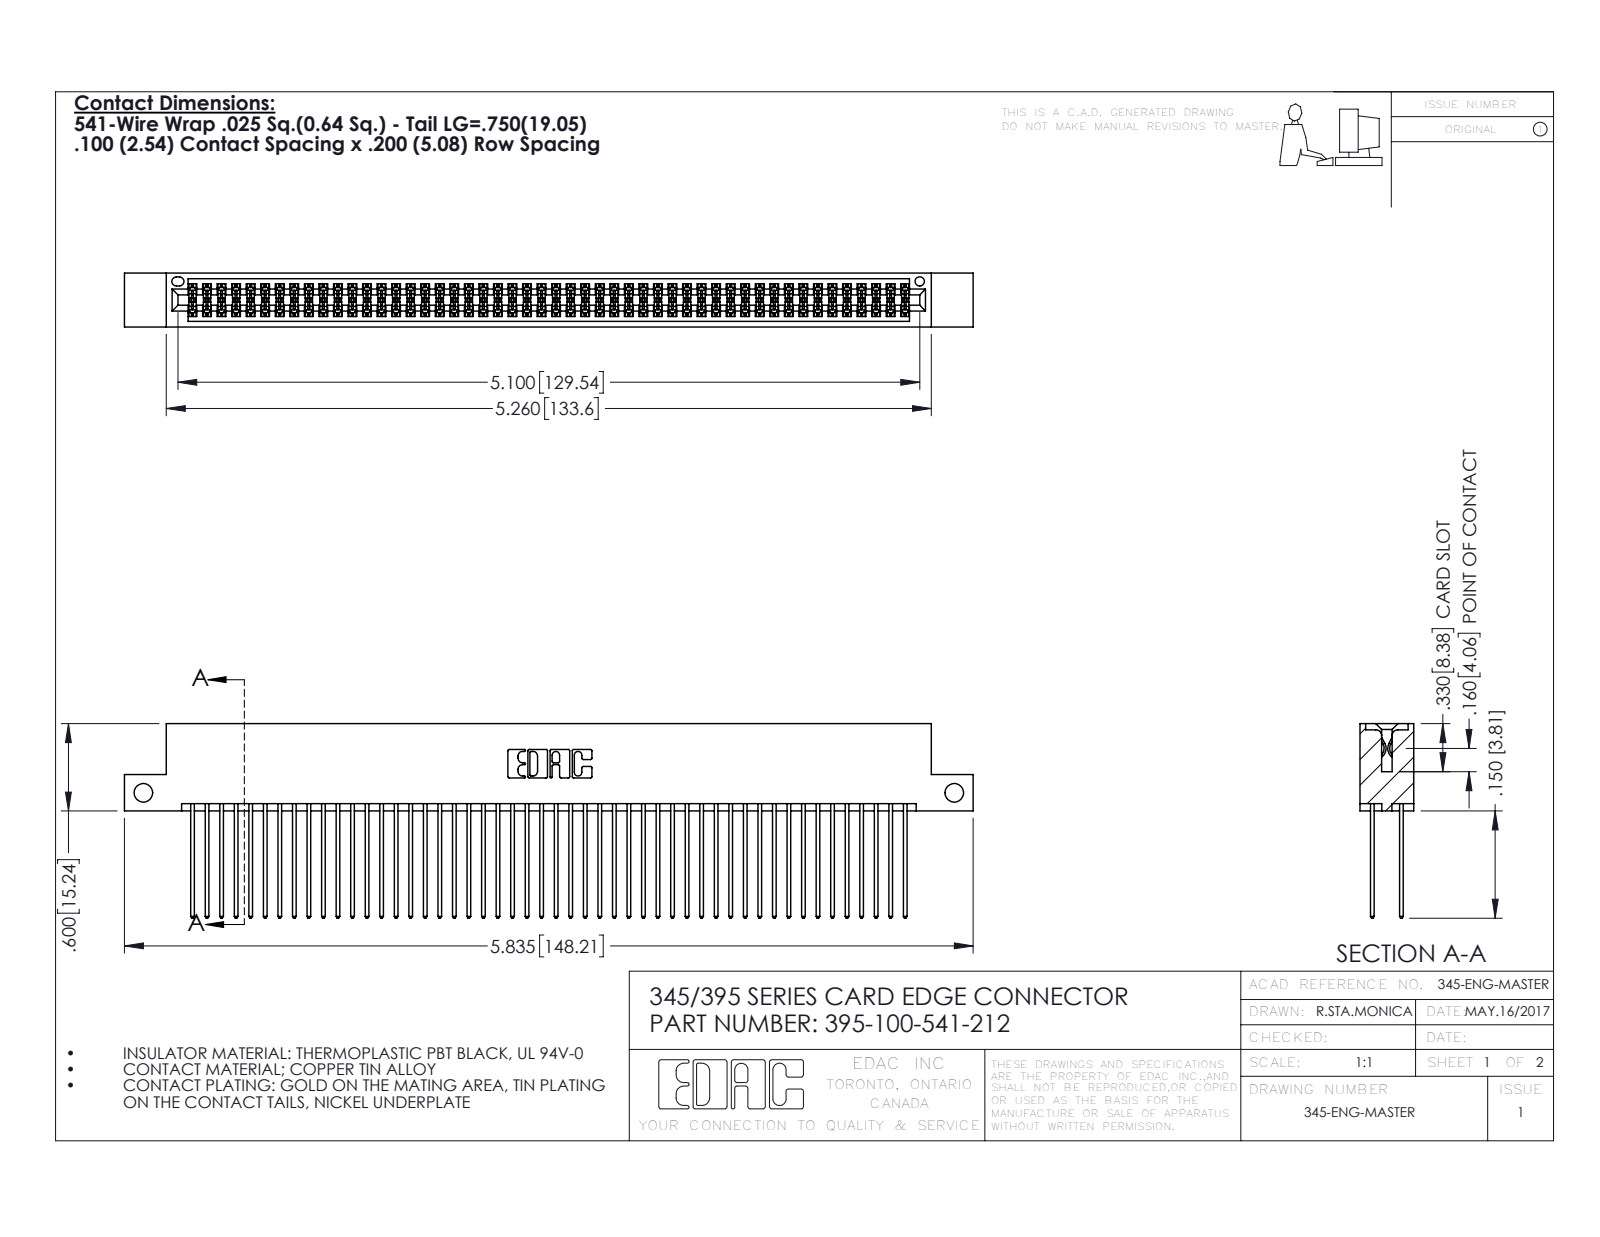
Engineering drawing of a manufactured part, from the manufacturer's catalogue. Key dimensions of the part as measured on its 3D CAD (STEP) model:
Part name (STEP PRODUCT): 345-292-001_345-293-141; 395-100-541-212; 345 Part_Flush Mounting Lugs - Side Mount
STEP written by: SolidWorks 2016 (CONFIG_CONTROL_DESIGN)
Units: inches
Bodies: 101 solids, 5126 faces (3380 planar, 1746 cylindrical, 0 other)
Overall size (bounding box): 5.835 × 1.337 × 0.37
Volume: 0.913 in³ · Surface area: 38.48 in²
Round holes (diameter × count): ⌀0.128 ×2, ⌀0.064 ×1
Partial cylindrical surfaces — rounded edges, fillets, slot ends (radius × count): R0.006 ×150, R0.01 ×100, R0.01 ×22, R0.007 ×6, R0.031 ×6, R0.026 ×3, R0.014 ×2, R0.019 ×2
Main face-to-face distances: 0.298, 0.072, 0.2, 0.098, 0.272, 0.025, 0.225, 0.37, 0.175, 0.149
Hole centre spacings: 5.575
